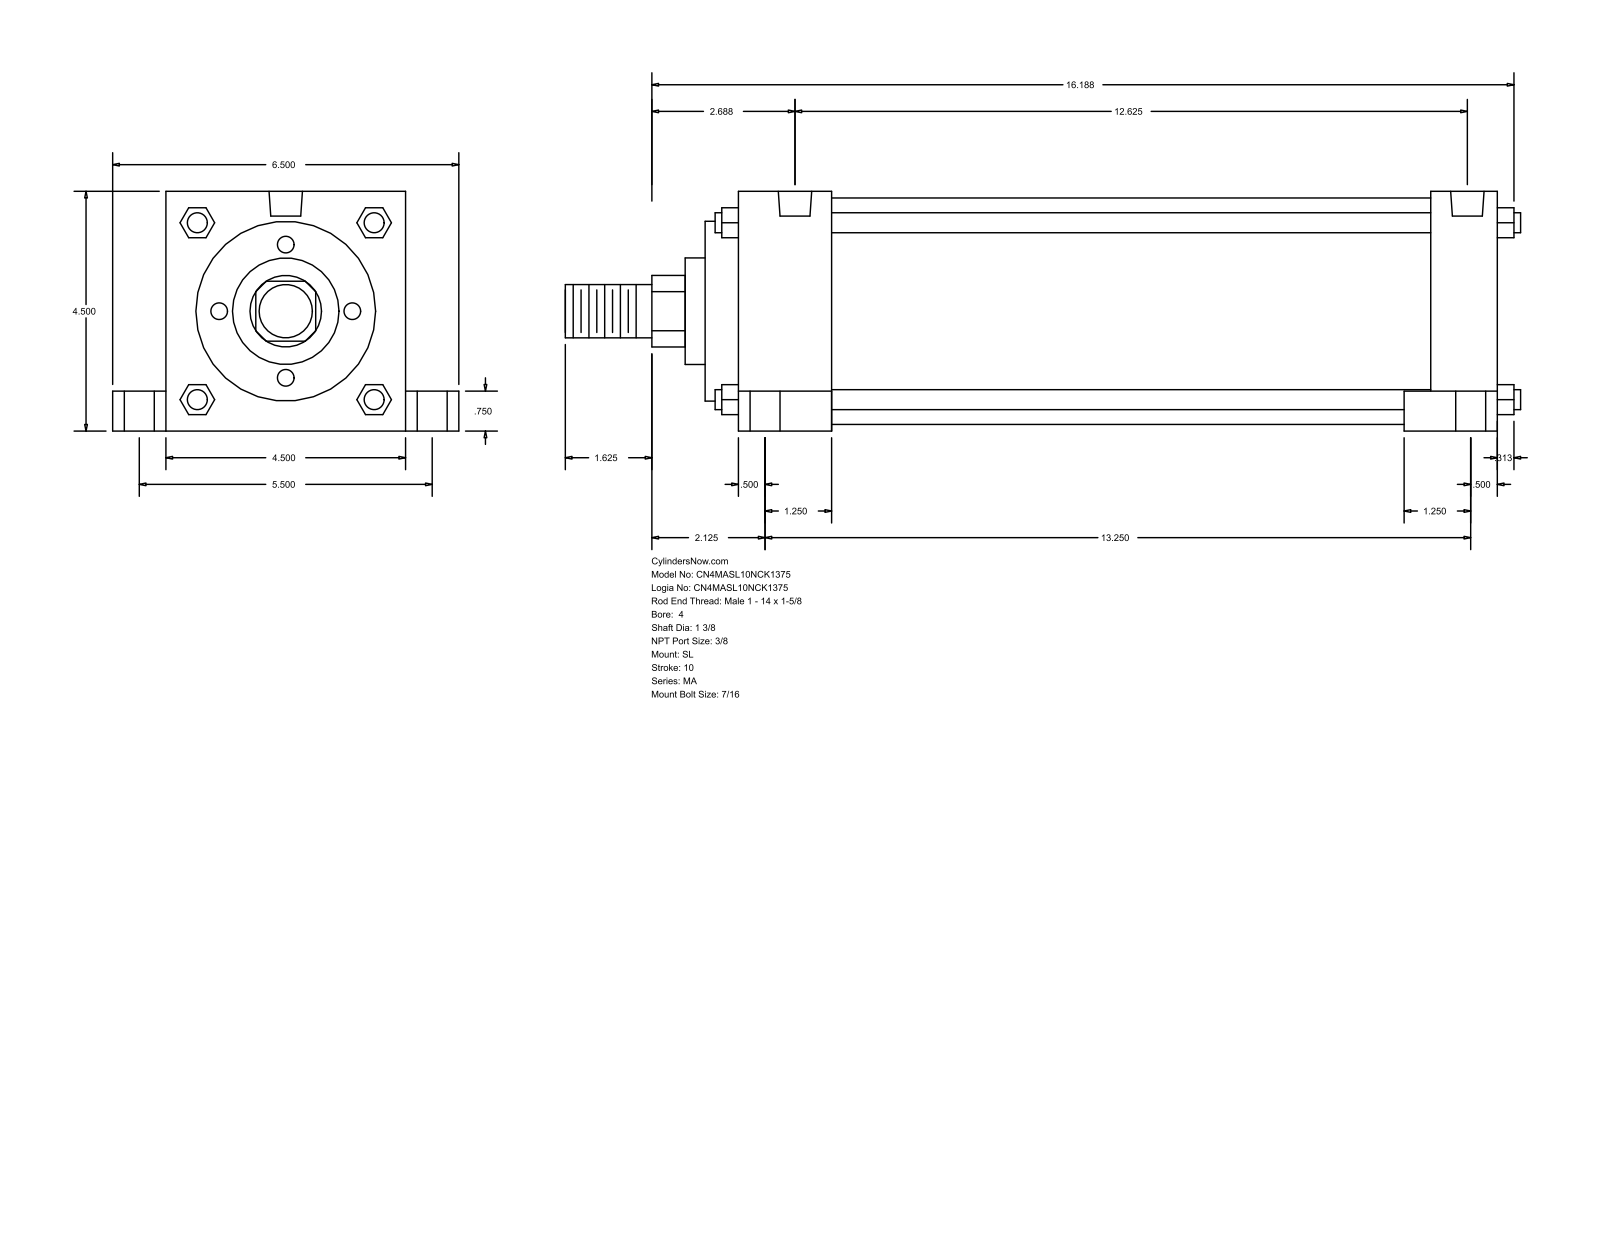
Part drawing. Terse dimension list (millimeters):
name: MA_SL__0400_1.375
written by: GSSL Pune (CONFIG_CONTROL_DESIGN)
unit: mm
bodies: 0 solids, 150 faces (113 planar, 37 cylindrical, 0 other)
size: 455.61 × 165.1 × 114.3
holes: 4× ⌀11.11, 4× ⌀14.29, 4× ⌀20.64, 2× ⌀15.93
bosses: 4× ⌀9.53, 1× ⌀107.95, 1× ⌀85.72, 1× ⌀50.8, 1× ⌀34.92, 1× ⌀25.4
rounds: 1× R17.06
face distances: 114.3, 361.96, 15.87, 377.83, 60.32, 44.45, 317.51, 346.08, 330.21, 285.76
hole spacings: 69.87, 70.14, 71.29, 72.4, 139.7, 311.15, 325.08, 329.74
